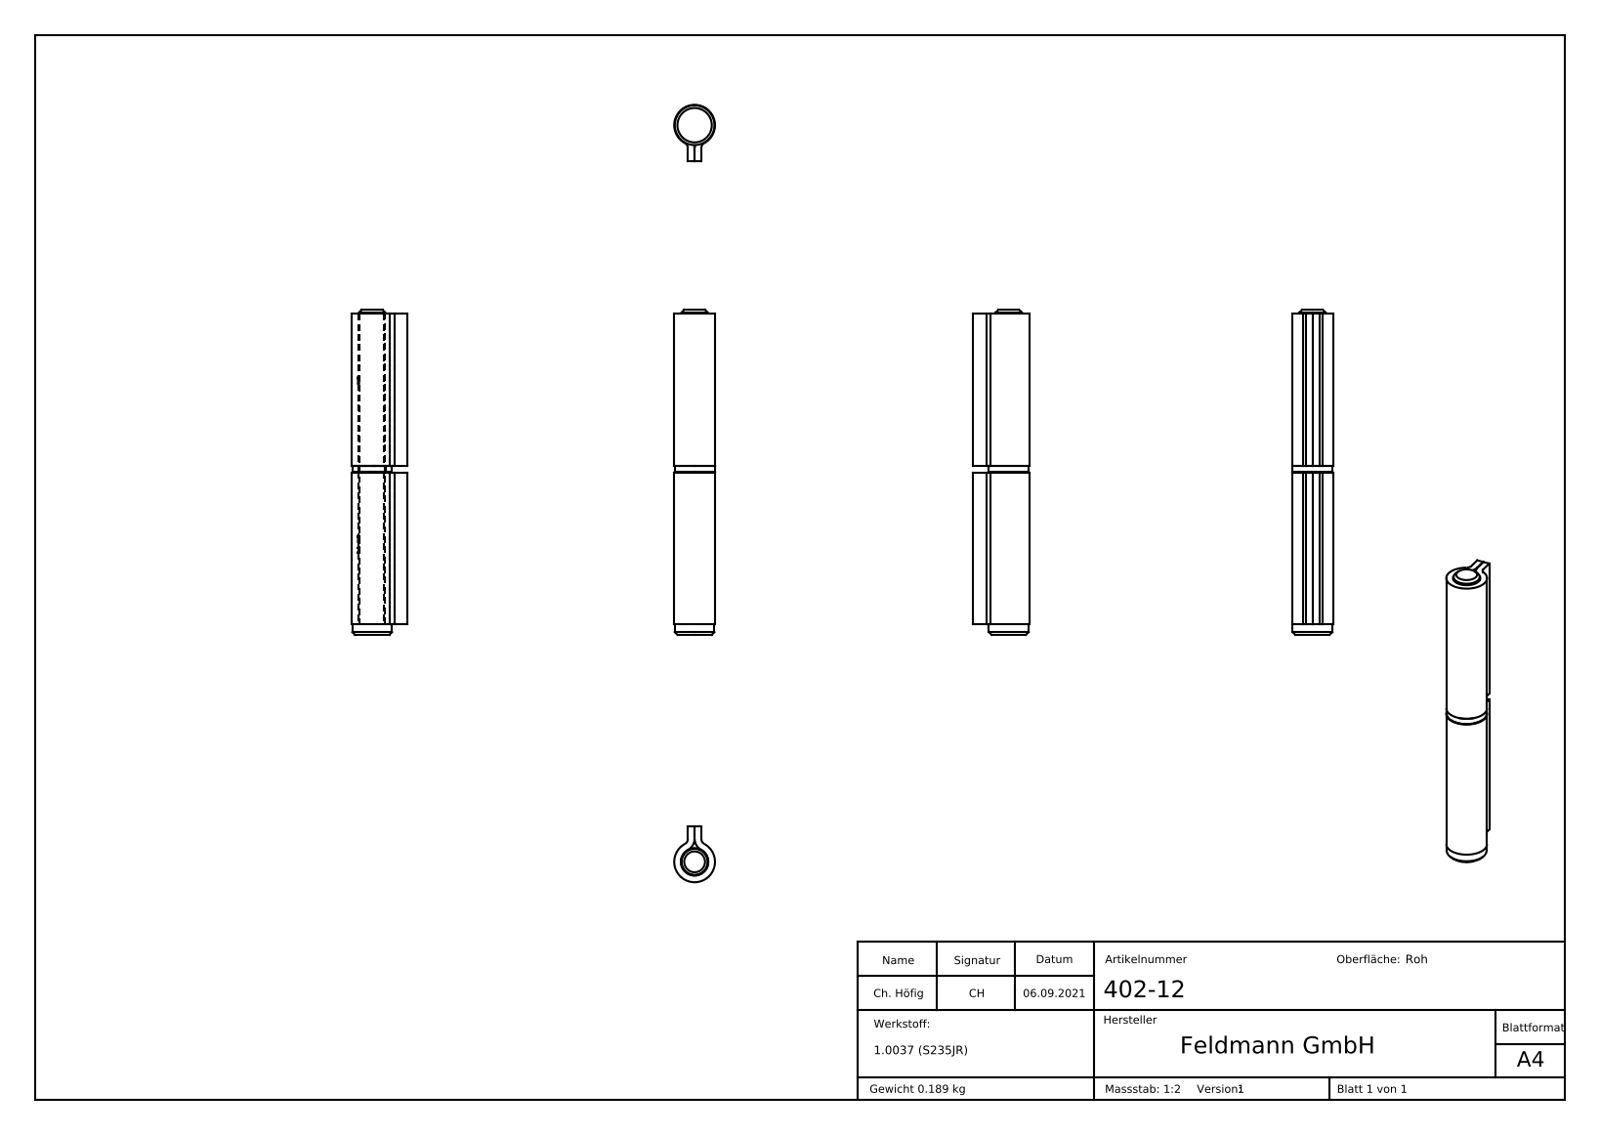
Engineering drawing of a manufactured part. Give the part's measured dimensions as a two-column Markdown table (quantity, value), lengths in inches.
| quantity | value |
| --- | --- |
| part name | 402-xx Teil2; 402-xx Teil4_402-12 Teil4; 402-12; 402-xx Teil1 (+5 more) |
| STEP written by | SolidWorks 2018 (CONFIG_CONTROL_DESIGN) |
| units | inches |
| bodies | 4 solids, 306 faces (154 planar, 37 cylindrical, 115 other) |
| overall size | 4.803 × 0.827 × 0.602 |
| volume | 1.479 in³ |
| surface area | 26.56 in² |
| round holes (diameter × count) | 0.394 × 1, 0.406 × 1 |
| round bosses / shafts (diameter × count) | 0.602 × 1, 0.591 × 1, 0.587 × 1, 0.386 × 1 |
| partial cylindrical surfaces (radius × count) | 0.079 × 2, 0.177 × 2, 0.207 × 1 |
| main face-to-face distances | 0.098, 0.102, 0.201, 2.343, 2.244, 2.402, 0.157, 2.5, 4.744, 4.587 |
